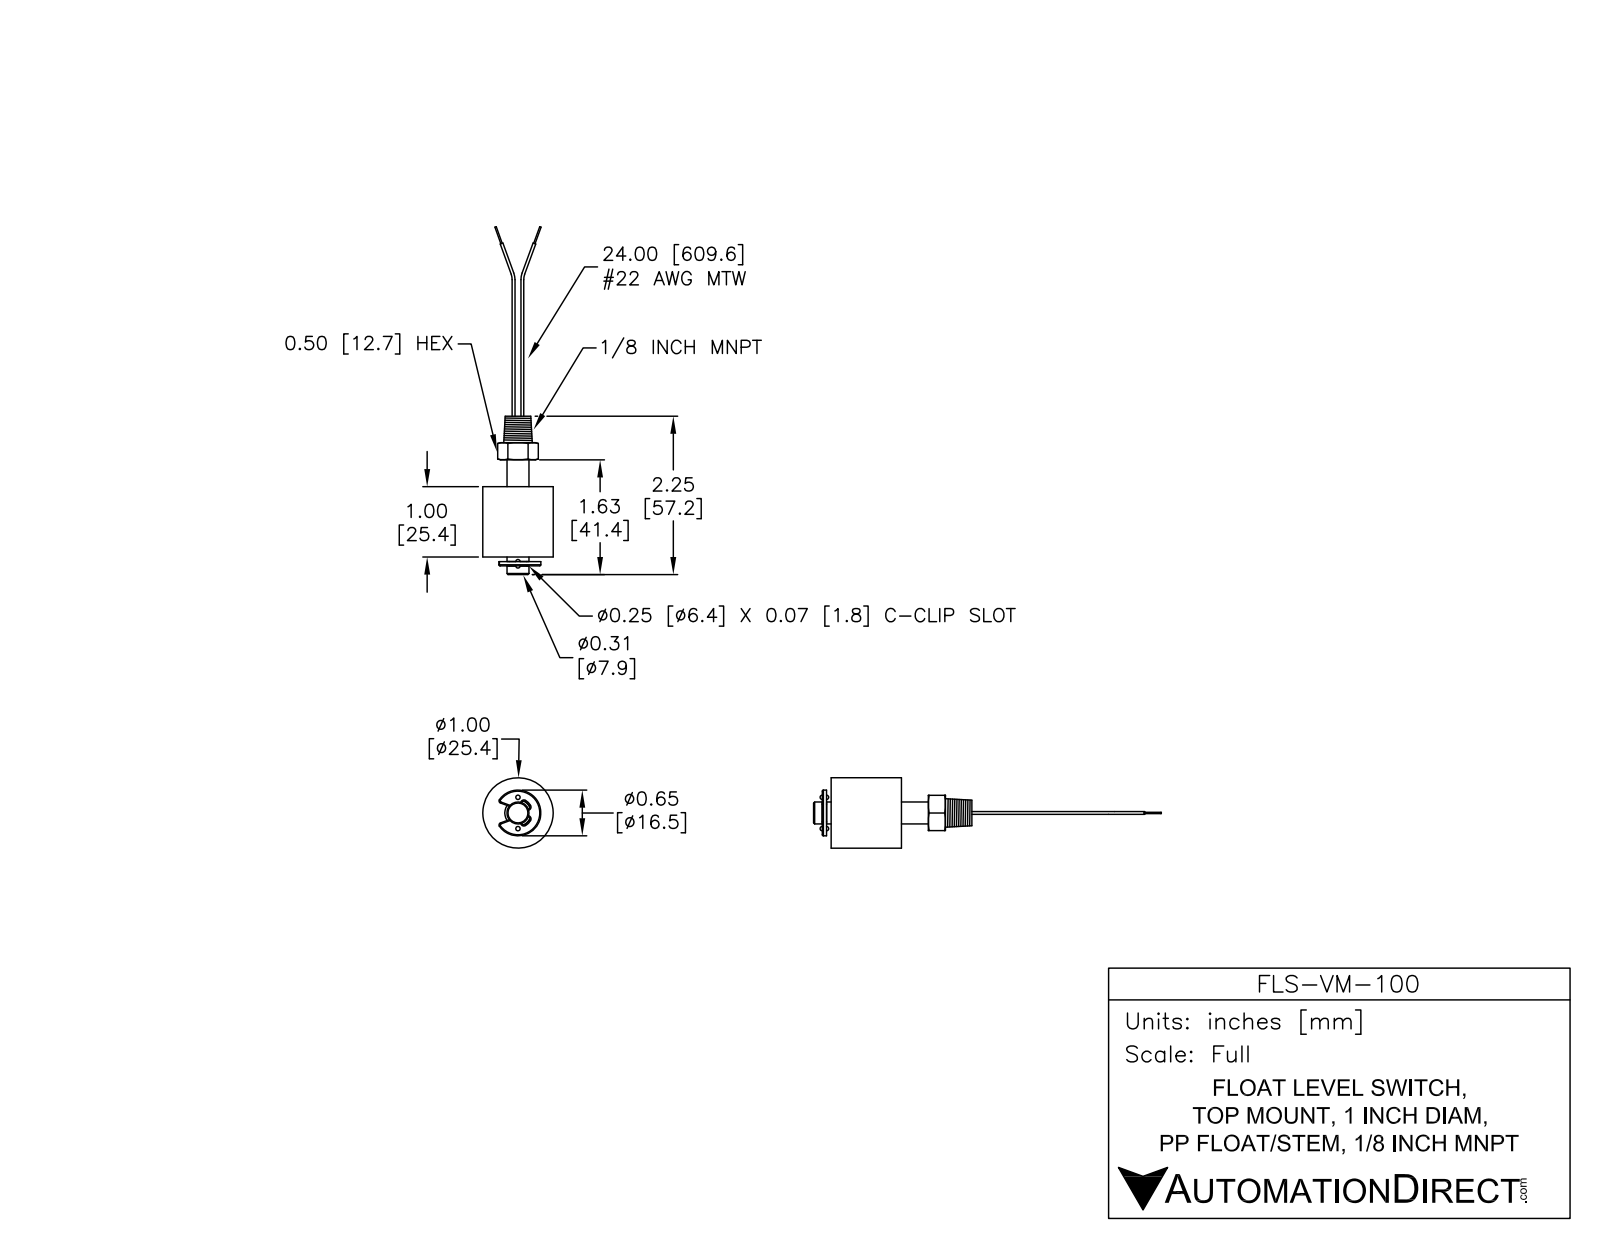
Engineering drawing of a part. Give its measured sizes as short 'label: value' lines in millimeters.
name: FLS-VM-100
written by: SolidWorks 2013 (AUTOMOTIVE_DESIGN)
unit: mm
bodies: 6 solids, 95 faces (33 planar, 46 cylindrical, 16 other)
size: 126.6 × 25.4 × 25.4
volume: 15 200 mm³; area: 6 735 mm²
holes: 1× ⌀9.7
bosses: 4× ⌀1, 2× ⌀0.5, 1× ⌀25.4, 1× ⌀16.5, 1× ⌀8, 1× ⌀8, 1× ⌀6.4
rounds: 8× R0.8, 4× R0.4, 1× R3.3, 1× R4.9
face distances: 25.4, 35, 9.6, 3.3, 28.7, 38.3, 1.5, 1.7, 27.1, 36.7
